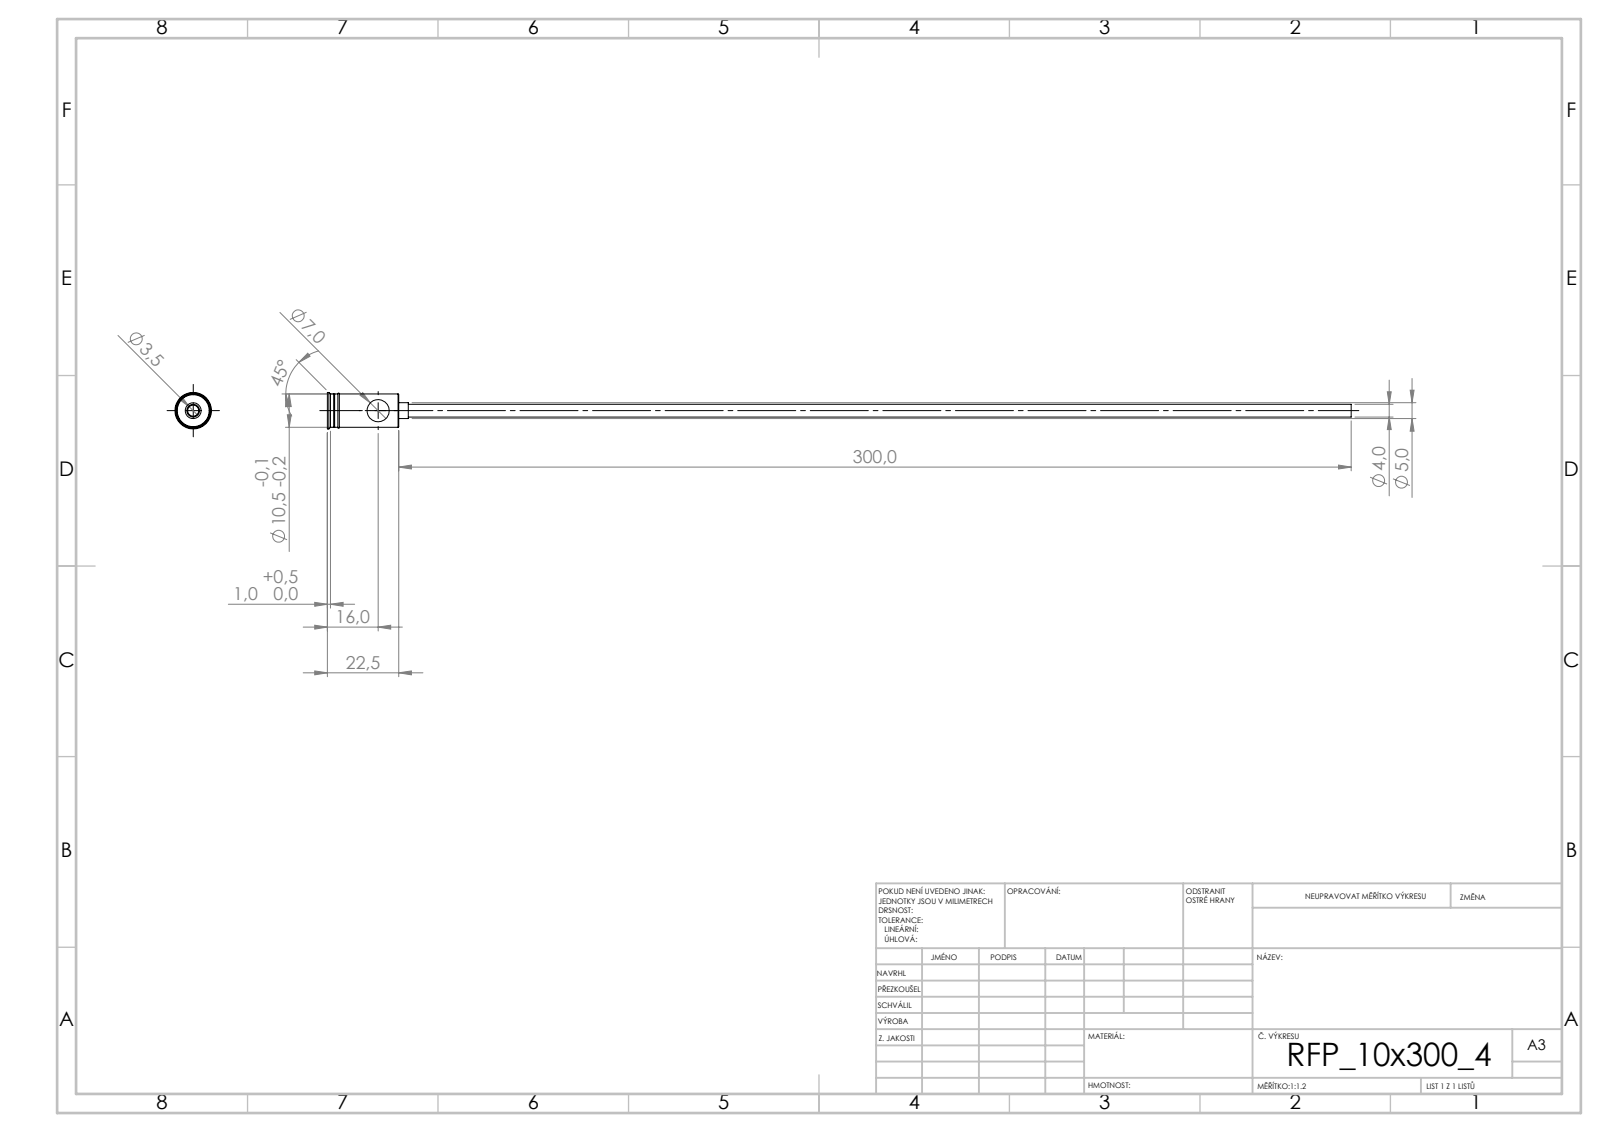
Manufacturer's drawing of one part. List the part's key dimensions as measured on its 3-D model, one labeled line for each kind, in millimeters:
STEP written by: SolidWorks 2019 (CONFIG_CONTROL_DESIGN)
Units: millimetres
Bodies: 1 solid, 44 faces (20 planar, 16 cylindrical, 8 other)
Overall size (bounding box): 322.5 × 11.5 × 11.5
Volume: 2 397 mm³ · Surface area: 8 218 mm²
Round holes (diameter × count): ⌀3.5 ×1, ⌀7 ×1
Round bosses / shafts (diameter × count): ⌀11.5 ×1, ⌀10.5 ×1, ⌀5 ×1, ⌀4 ×1
Main face-to-face distances: 22.5, 20.5, 2, 5.9, 20.2, 2.3, 3, 23.2, 23.5, 25.5
